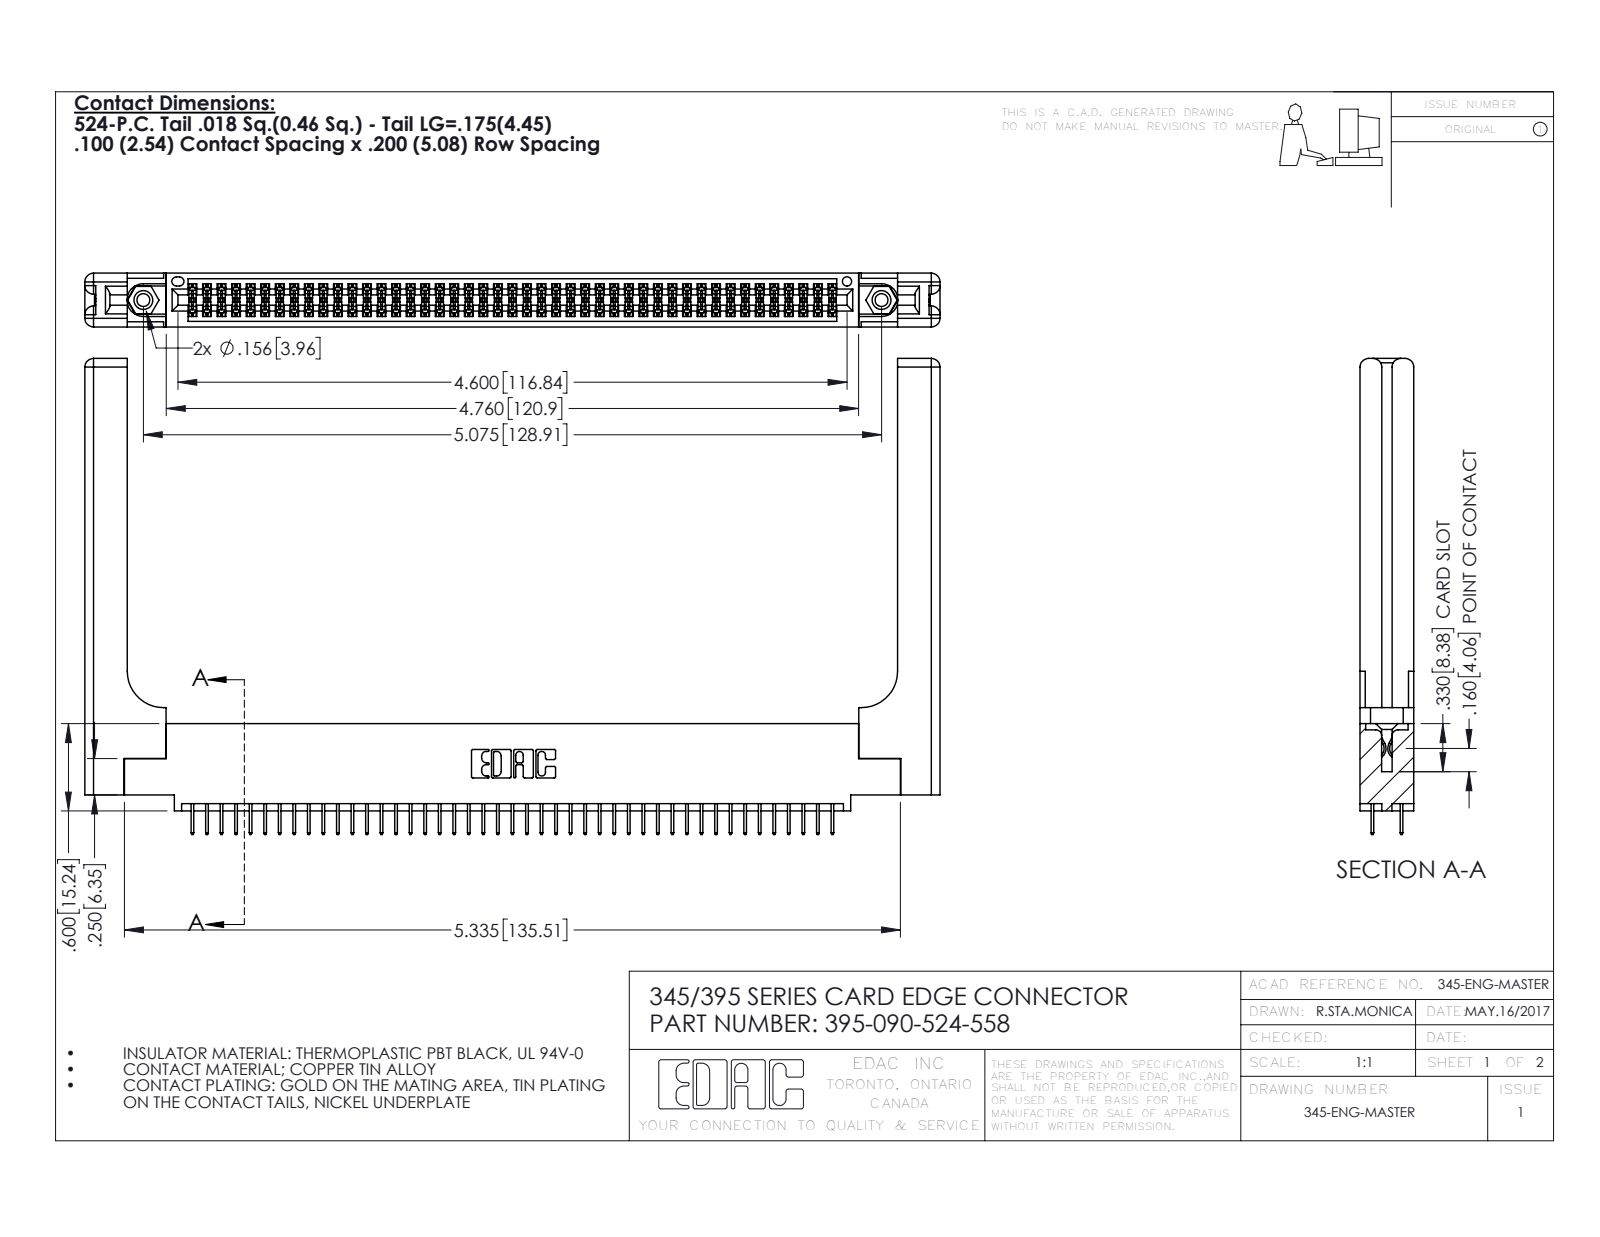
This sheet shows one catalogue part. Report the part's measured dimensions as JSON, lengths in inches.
{"part_name": "345-220-058_345-220-058; 395-090-524-558; 345 Part_0.110 Offset - 0.156 Dia-TH; 345-250-001_345-250-001-102 (+1 more)", "step_written_by": "SolidWorks 2016 (CONFIG_CONTROL_DESIGN)", "units": "inches", "bodies": {"solids": 95, "faces": 5246, "planar": 3742, "cylindrical": 1444, "other": 60}, "overall_size": [5.879, 3.272, 0.37], "volume_in3": 1.391, "surface_area_in2": 40.34, "round_holes": [[0.089, 2], [0.125, 2], [0.156, 2], [0.064, 1]], "round_bosses_or_shafts": [[0.155, 2]], "partial_cylinders_radius": [[0.006, 135], [0.01, 22], [0.06, 16], [0.007, 6], [0.031, 6], [0.026, 3], [0.014, 2], [0.019, 2]], "face_to_face_distances": [0.072, 0.37, 0.298, 0.2, 0.098, 0.272, 0.025, 0.225, 0.148, 0.15], "hole_center_spacings": [0.27, 4.839, 5.075]}
